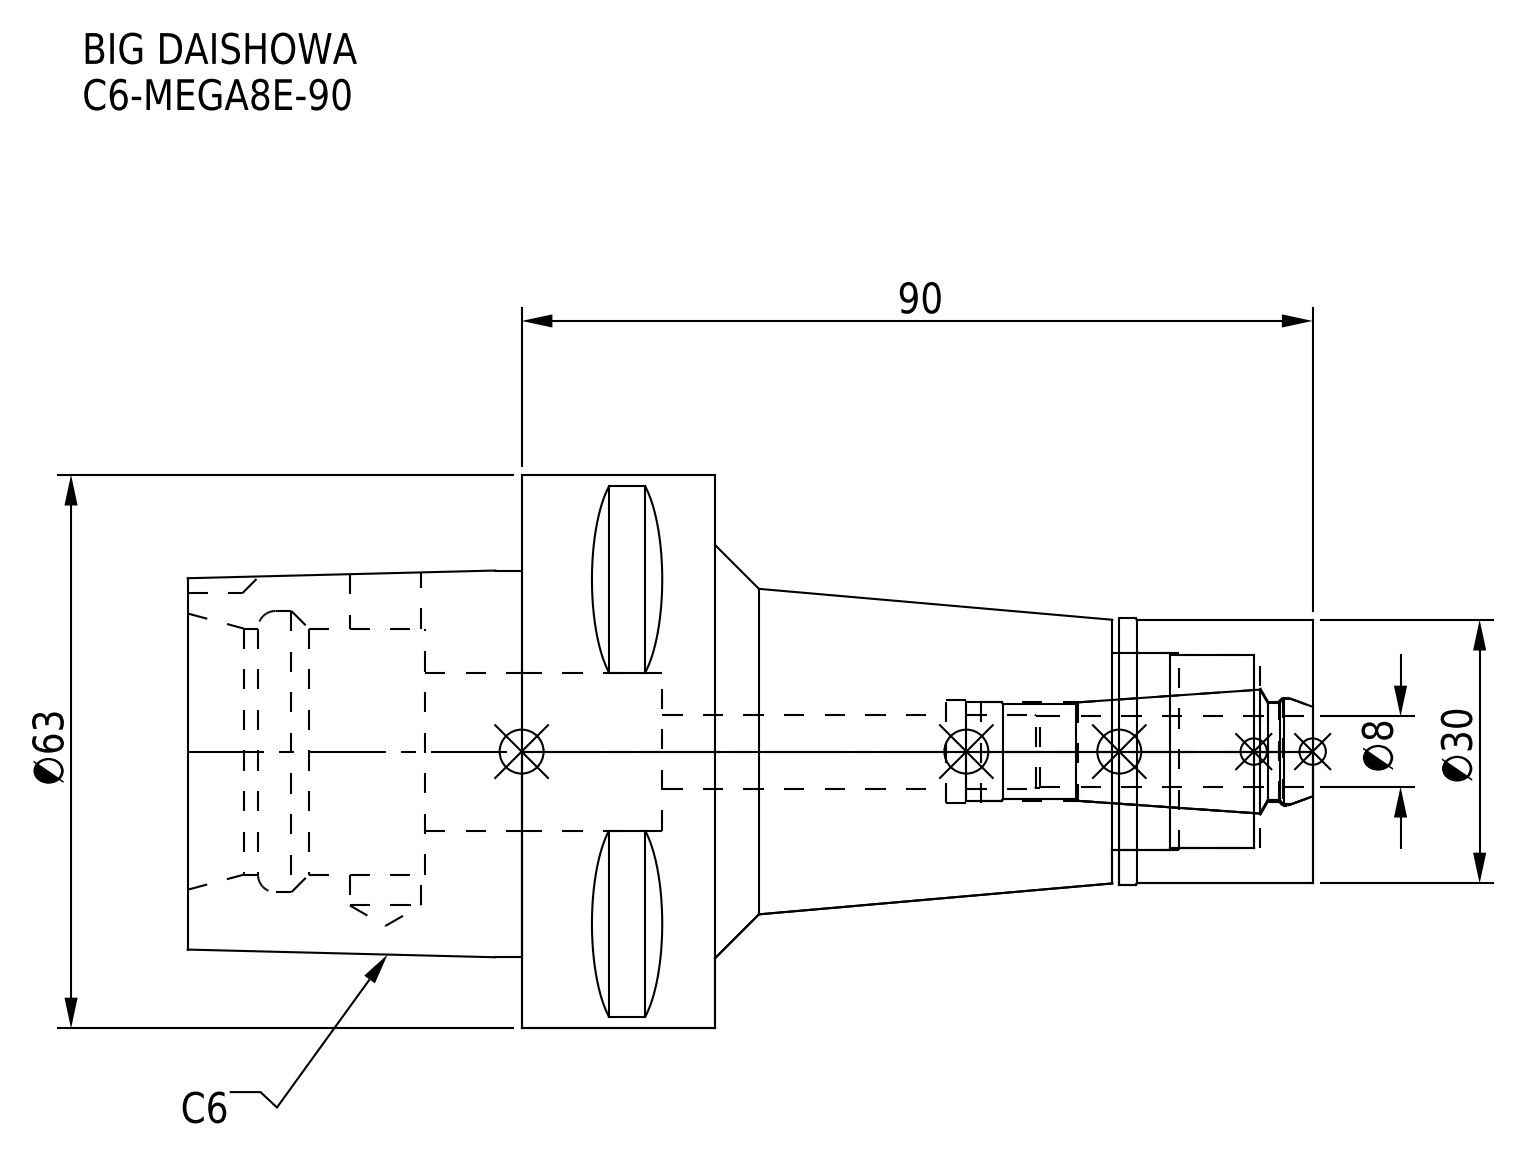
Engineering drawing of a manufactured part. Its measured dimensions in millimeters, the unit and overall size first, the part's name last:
Units: millimetres
Overall size (bounding box): 128 × 63 × 63
Round holes (diameter × count): ⌀8.1 ×1, ⌀8.4 ×1, ⌀11.2 ×1, ⌀11.4 ×1, ⌀11.8 ×1, ⌀12.3 ×1, ⌀18 ×1, ⌀22 ×1, ⌀22.5 ×1, ⌀28 ×1, ⌀32 ×1
Round bosses / shafts (diameter × count): ⌀63 ×1, ⌀30.3 ×1, ⌀30 ×1
Partial cylindrical surfaces — rounded edges, fillets, slot ends (radius × count): R5 ×1
Main face-to-face distances: 22, 68, 90, 27, 128, 60, 38, 6, 16, 101
Volume: 148 306 mm³ · Surface area: 32 102 mm²
Bodies: 2 solids, 97 faces (36 planar, 37 cylindrical, 24 other)
Part name (STEP PRODUCT): C6-MEGA8E-90; C6-MEGA8E-90_1.stp; DXF_TEMP_ASSY_ASM_4_ASM.stp; MEN8_1.stp (+3 more)
STEP written by: SolidWorks 2019 (CONFIG_CONTROL_DESIGN)
